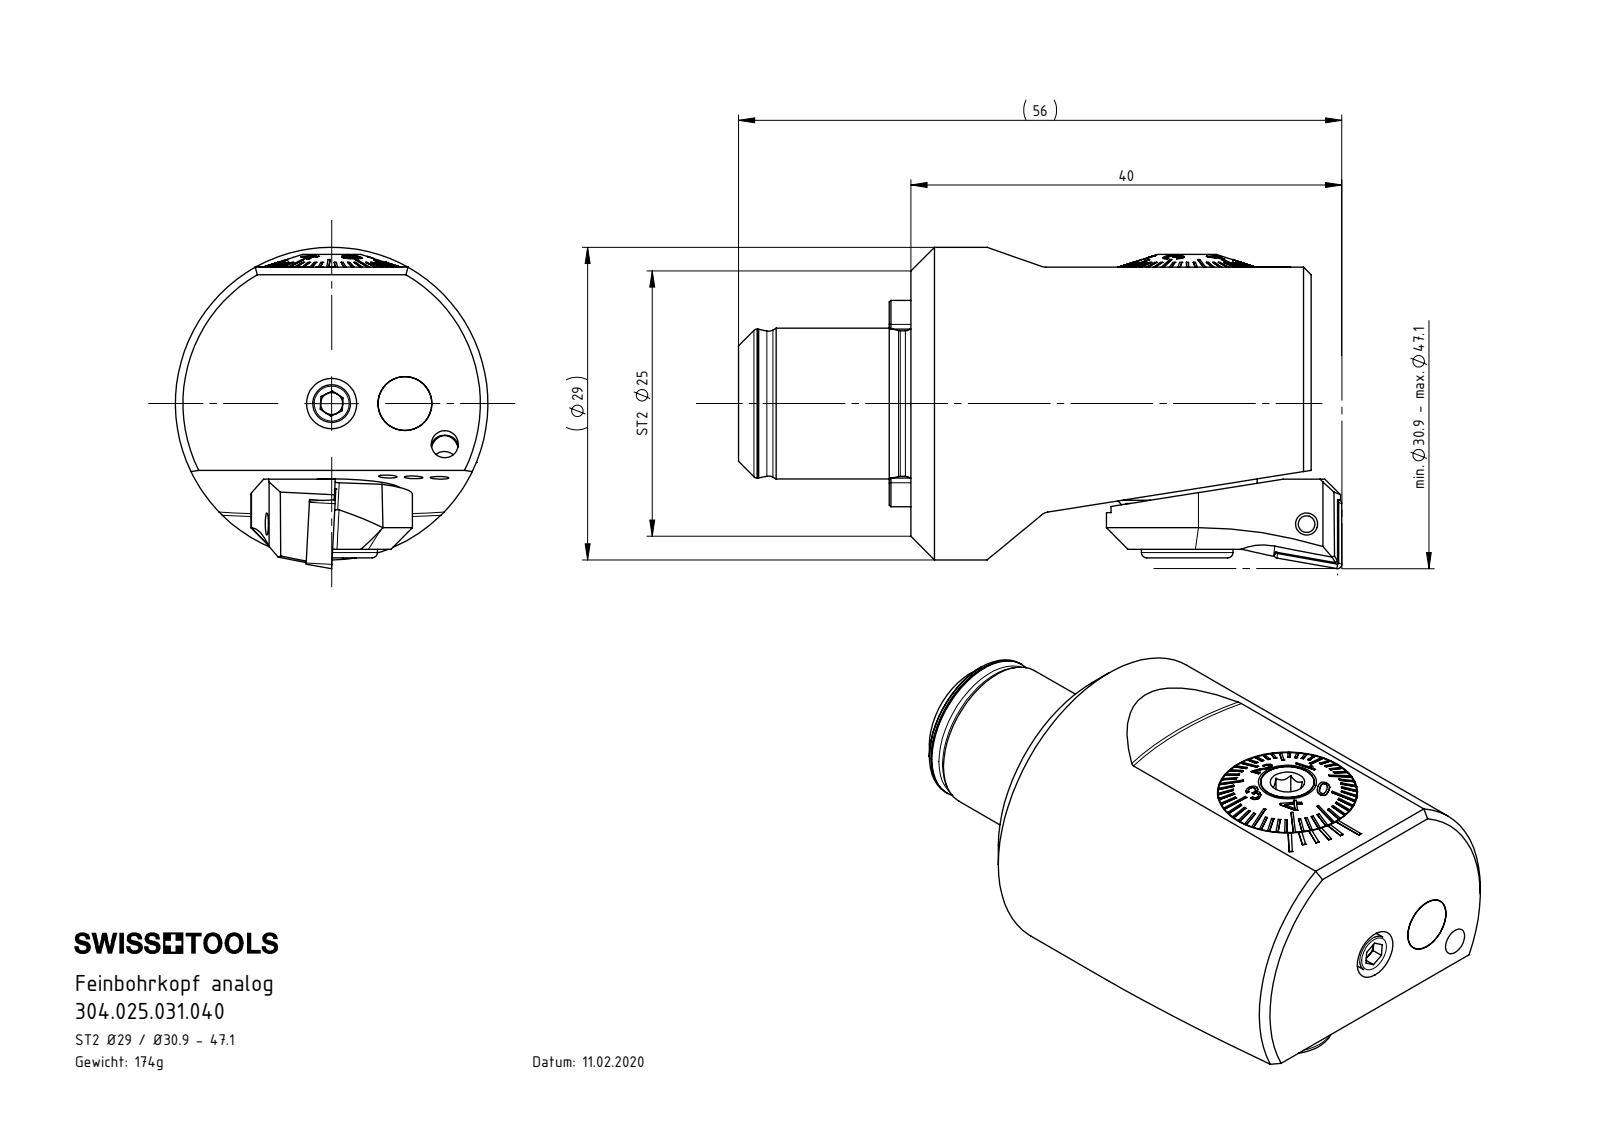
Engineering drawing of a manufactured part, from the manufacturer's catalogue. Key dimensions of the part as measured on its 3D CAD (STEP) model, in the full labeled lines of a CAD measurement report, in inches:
Part name (STEP PRODUCT): F25-BG1.002.013_C; F25-BG1.009.006_A; Klebstoff D5; ISO 4026 - M5 x 4_PreviewCfg (+8 more)
STEP written by: SolidWorks 2015 (CONFIG_CONTROL_DESIGN)
Units: inches
Bodies: 20 solids, 864 faces (349 planar, 174 cylindrical, 341 other)
Overall size (bounding box): 2.205 × 1.105 × 0.984
Volume: 1.155 in³ · Surface area: 17.59 in²
Round holes (diameter × count): ⌀0.079 ×5, ⌀0.081 ×2, ⌀0.087 ×2, ⌀0.165 ×2, ⌀0.197 ×2, ⌀0.083 ×1, ⌀0.094 ×1, ⌀0.106 ×1, ⌀0.11 ×1, ⌀0.118 ×1, ⌀0.13 ×1, ⌀0.152 ×1
Round bosses / shafts (diameter × count): ⌀0.087 ×3, ⌀0.197 ×2, ⌀0.195 ×2, ⌀0.098 ×2, ⌀0.984 ×1, ⌀0.551 ×1, ⌀0.543 ×1, ⌀0.531 ×1
Partial cylindrical surfaces — rounded edges, fillets, slot ends (radius × count): R0.02 ×8, R0.008 ×6, R0.014 ×5, R0.052 ×2, R0.078 ×2, R0.008 ×1, R0.014 ×1, R0.041 ×1
Main face-to-face distances: 1.463, 0.059, 0.785, 0.122, 0.618, 0.786, 0.168, 0.74, 0.046, 0.167
Hole centre spacings: 0.33, 0.425, 0.151, 0.157, 0.161, 0.268, 0.35, 0.361
